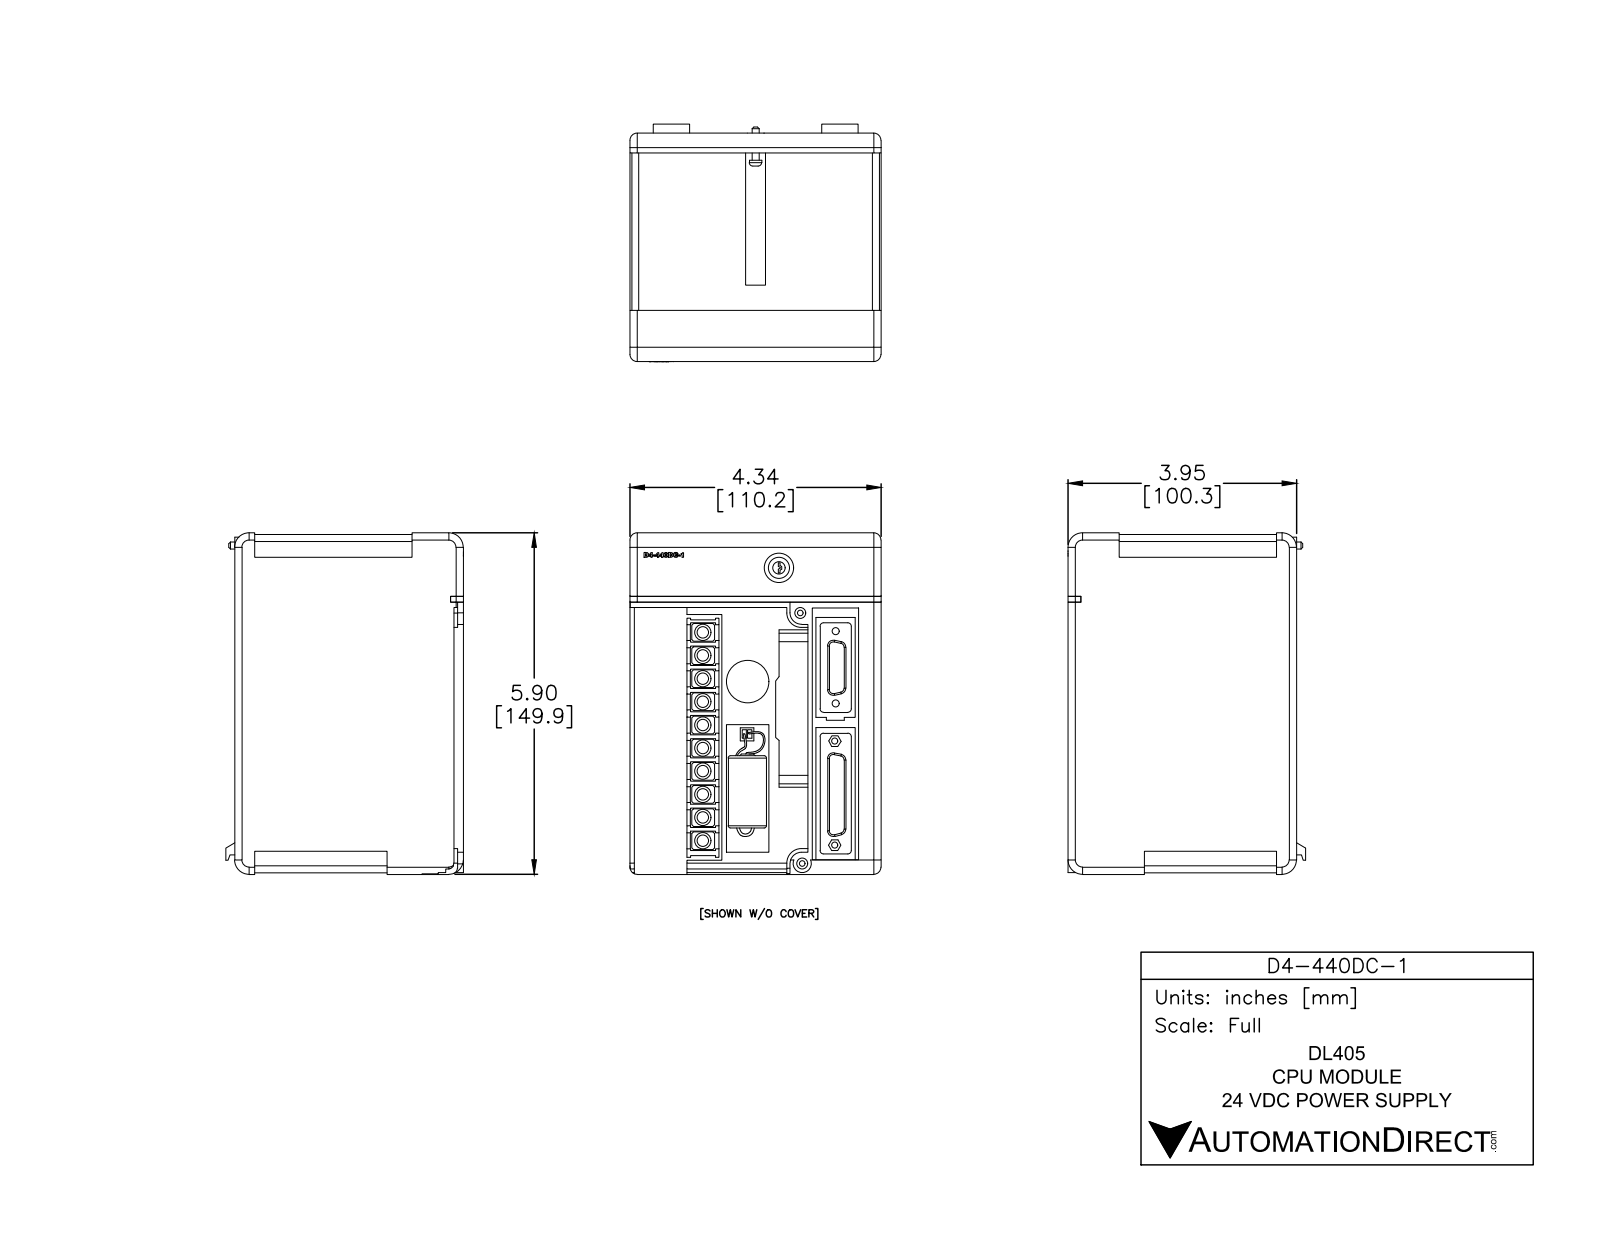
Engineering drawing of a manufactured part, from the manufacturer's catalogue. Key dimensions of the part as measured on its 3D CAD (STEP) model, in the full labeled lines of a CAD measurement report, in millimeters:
Part name (STEP PRODUCT): D4-440DC-1
STEP written by: SolidWorks 2014 (AUTOMOTIVE_DESIGN)
Units: millimetres
Bodies: 2 solids, 810 faces (592 planar, 130 cylindrical, 88 other)
Overall size (bounding box): 150 × 110.2 × 104.3
Volume: 1 487 000 mm³ · Surface area: 115 100 mm²
Round holes (diameter × count): ⌀2.5 ×2, ⌀3 ×2, ⌀2.6 ×1, ⌀2.7 ×1, ⌀4.8 ×1, ⌀4.8 ×1, ⌀5.5 ×1, ⌀13 ×1, ⌀18.5 ×1
Round bosses / shafts (diameter × count): ⌀7.1 ×10, ⌀1.4 ×5, ⌀1.4 ×4, ⌀16.8 ×1, ⌀9.3 ×1, ⌀5.4 ×1, ⌀3.1 ×1
Partial cylindrical surfaces — rounded edges, fillets, slot ends (radius × count): R2.5 ×9, R1.5 ×8, R3.2 ×8, R0.8 ×6, R6.4 ×6, R3 ×4, R5.1 ×2, R3.7 ×1
Main face-to-face distances: 110.2, 0.8, 148.5, 149.2, 100.3, 18.2, 82.2, 11.4, 96.3, 14.1
Hole centre spacings: 16.4, 16.5, 17.5, 21.9, 31.7, 37.3, 38, 39.9
